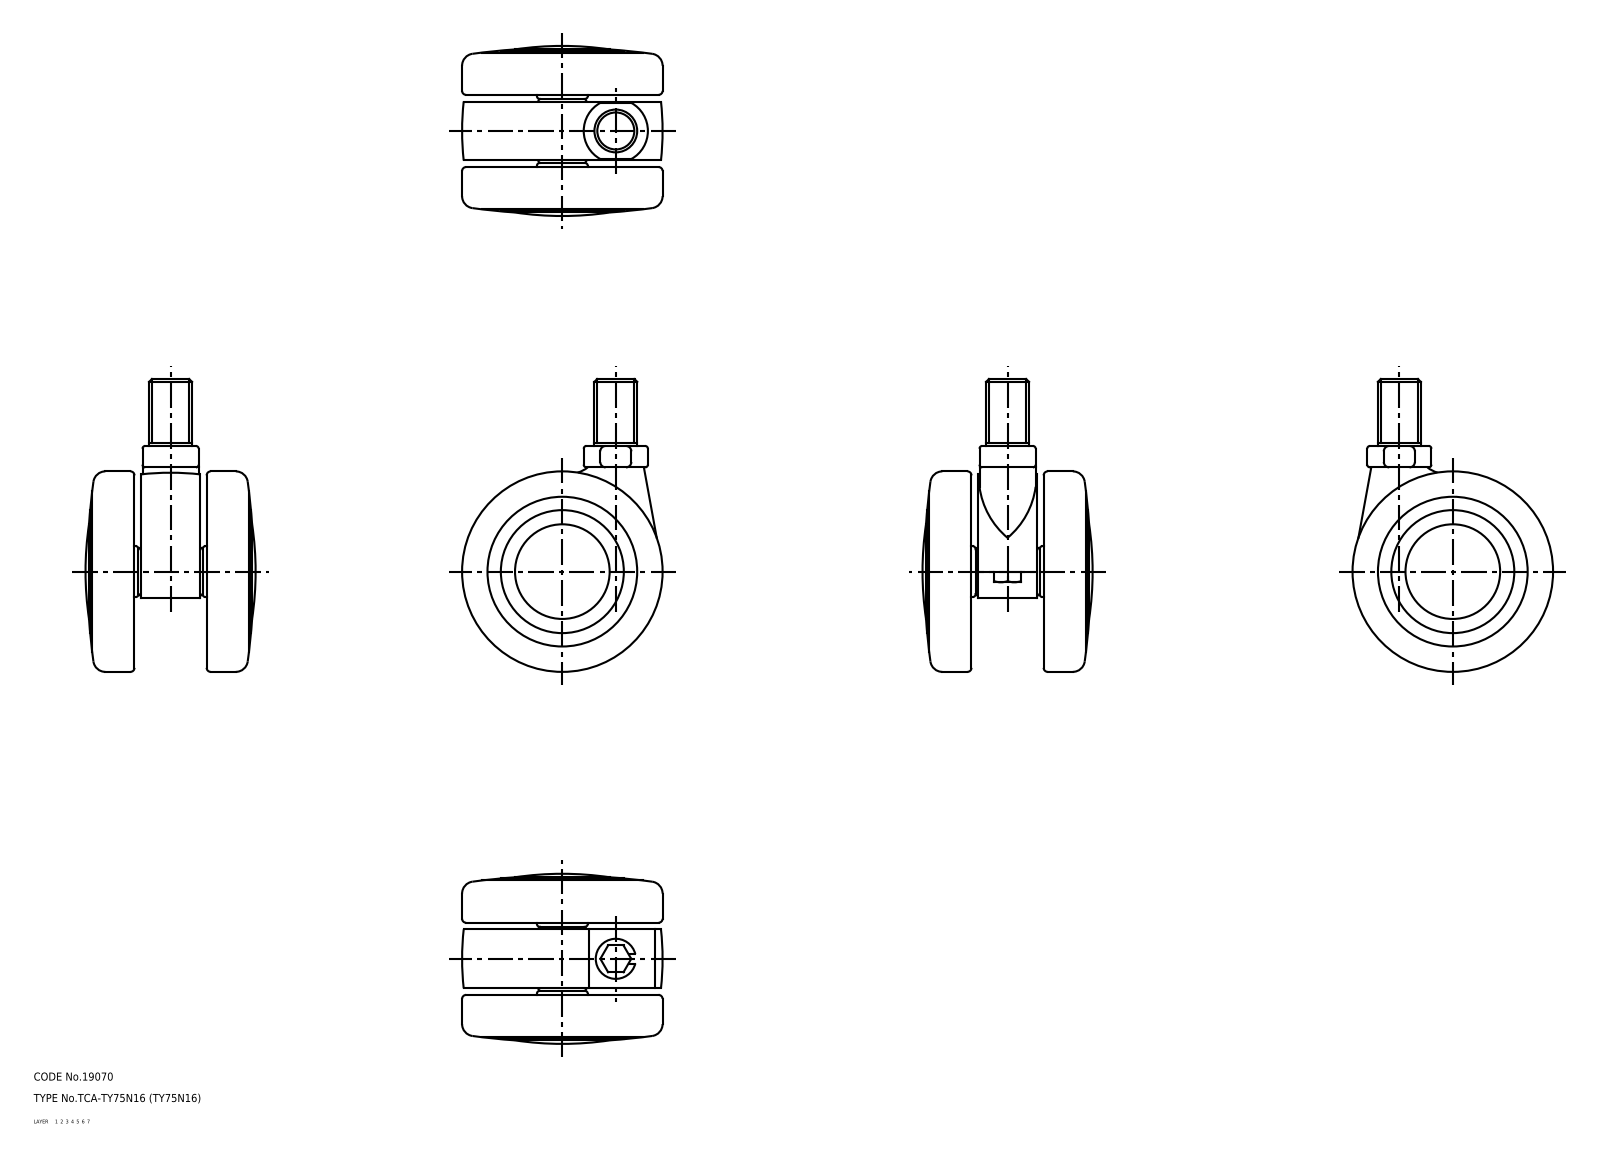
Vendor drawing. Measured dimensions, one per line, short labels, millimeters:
name: wheel_mr; wheel; main shaft; TY75N16_5799_36
written by: CADfix (AUTOMOTIVE_DESIGN)
unit: mm
bodies: 4 solids, 130 faces (0 planar, 0 cylindrical, 130 other)
size: 109.5 × 75 × 63.62
volume: 190 545 mm³; area: 49 495 mm²
